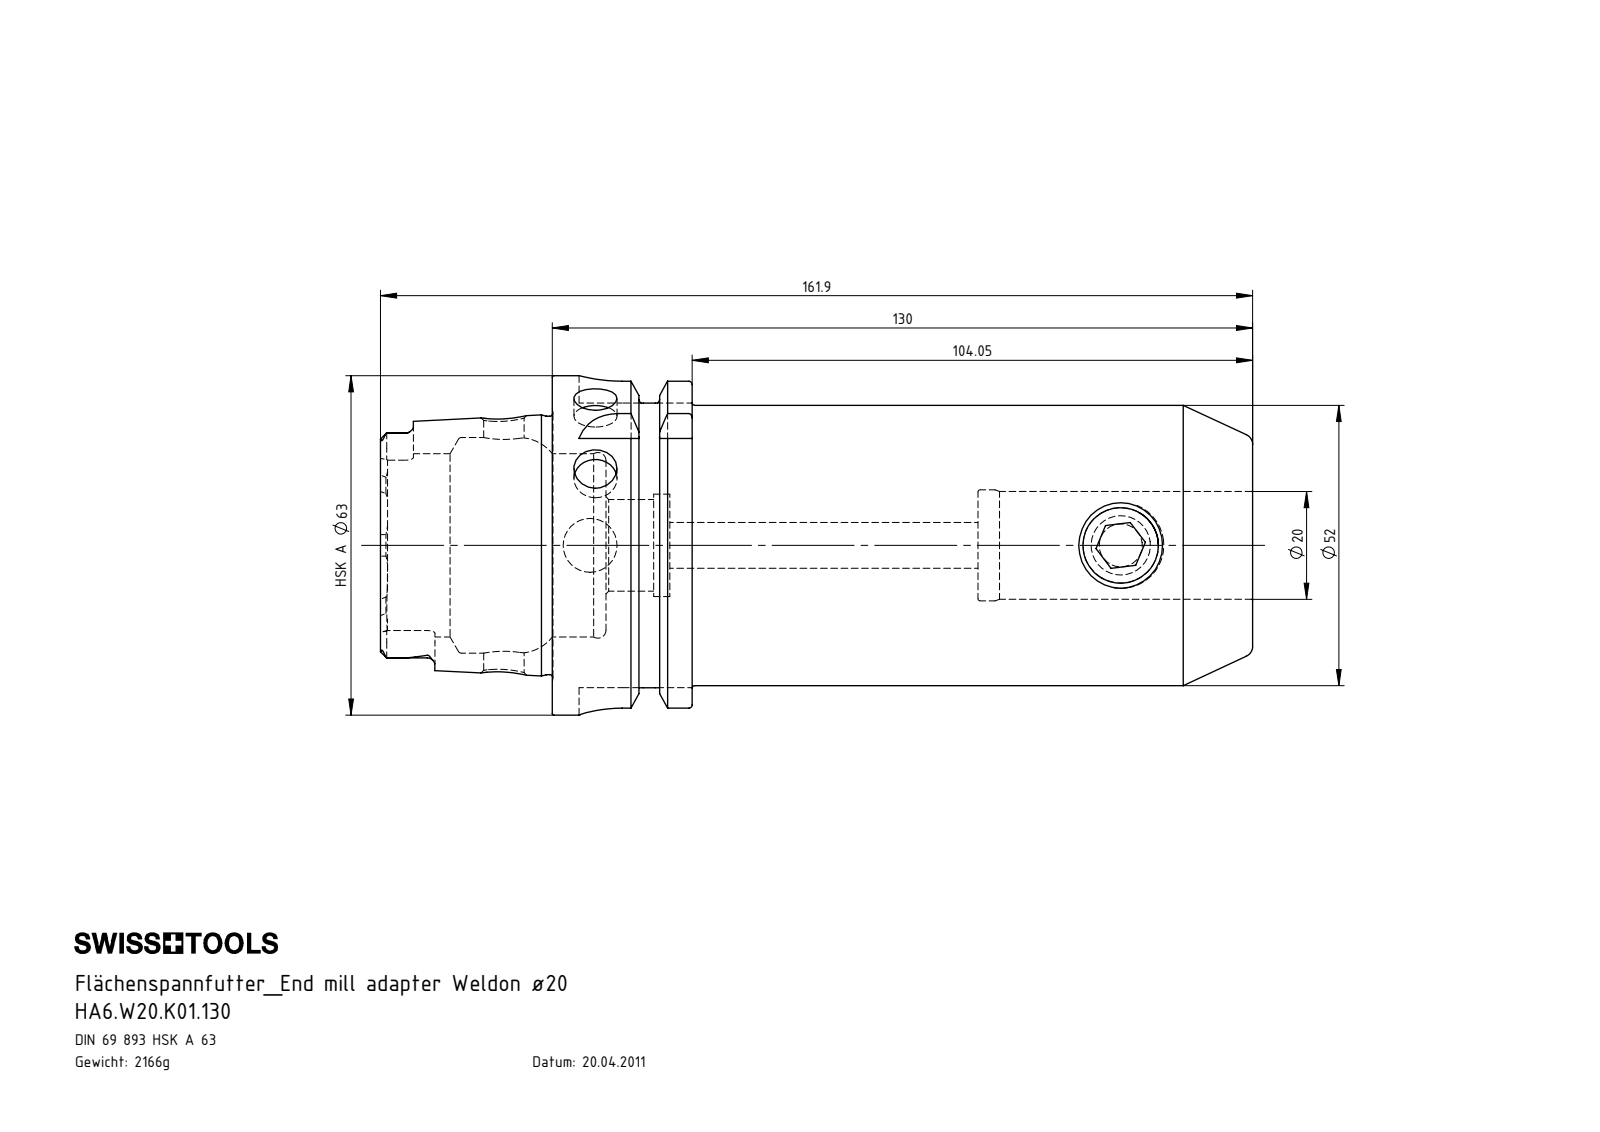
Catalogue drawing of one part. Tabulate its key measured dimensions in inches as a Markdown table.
| quantity | value |
| --- | --- |
| part name | HA6-W20.K01.130; W20-ER1.001.016; HA6-W20.K01.130_A_Fertigbearbeitung |
| STEP written by | SolidWorks 2012 (CONFIG_CONTROL_DESIGN) |
| units | inches |
| bodies | 2 solids, 209 faces (59 planar, 57 cylindrical, 93 other) |
| overall size | 6.374 × 2.48 × 2.48 |
| volume | 16.83 in³ |
| surface area | 69.78 in² |
| round holes (diameter × count) | 0.315 × 2, 0.295 × 1, 0.335 × 1, 0.394 × 1, 0.551 × 1, 0.669 × 1, 0.748 × 1, 0.787 × 1, 0.811 × 1, 1.339 × 1, 1.575 × 1 |
| round bosses / shafts (diameter × count) | 2.48 × 1, 2.163 × 1, 2.047 × 1, 1.887 × 1, 0.63 × 1 |
| partial cylindrical surfaces (radius × count) | 0.055 × 6, 0.113 × 4, 0.315 × 4 |
| main face-to-face distances | 5.118, 1.022, 4.096, 0.63, 0.392, 4.726, 1.256, 1.648, 2.278, 6.374 |
| hole center spacings | 3.878 |
